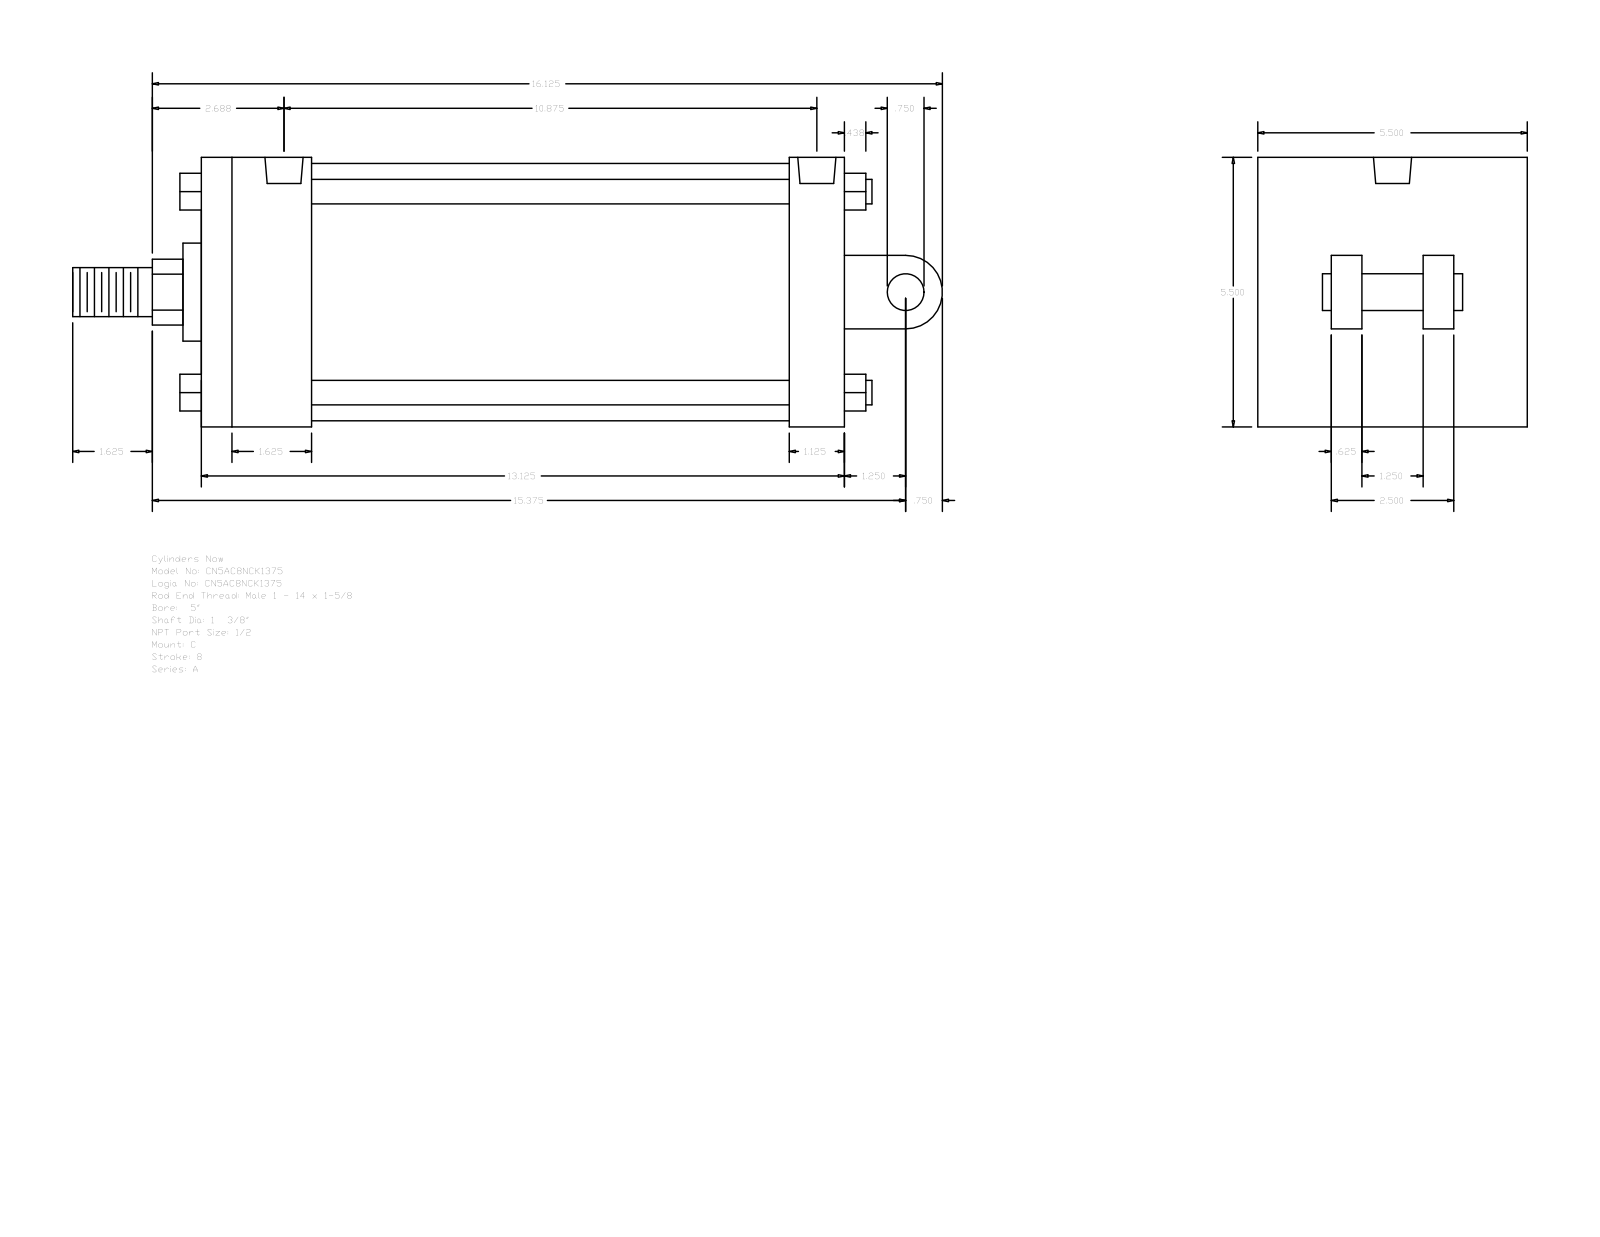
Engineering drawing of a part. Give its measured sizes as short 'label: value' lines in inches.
name: A_C__0500_1.375
written by: GSSL Pune (CONFIG_CONTROL_DESIGN)
unit: in
bodies: 0 solids, 135 faces (102 planar, 33 cylindrical, 0 other)
size: 17.75 × 5.5 × 5.5
holes: 4× ⌀0.344, 2× ⌀0.778
bosses: 4× ⌀0.5, 1× ⌀5.25, 1× ⌀2, 1× ⌀1.375, 1× ⌀1, 1× ⌀0.75
rounds: 1× R0.672, 1× R0.75
face distances: 5.5, 13.125, 2.25, 12, 9.75, 10.875, 1.125, 1.5, 2.125, 4
hole spacings: 0.094, 10.687, 10.781, 10.875
